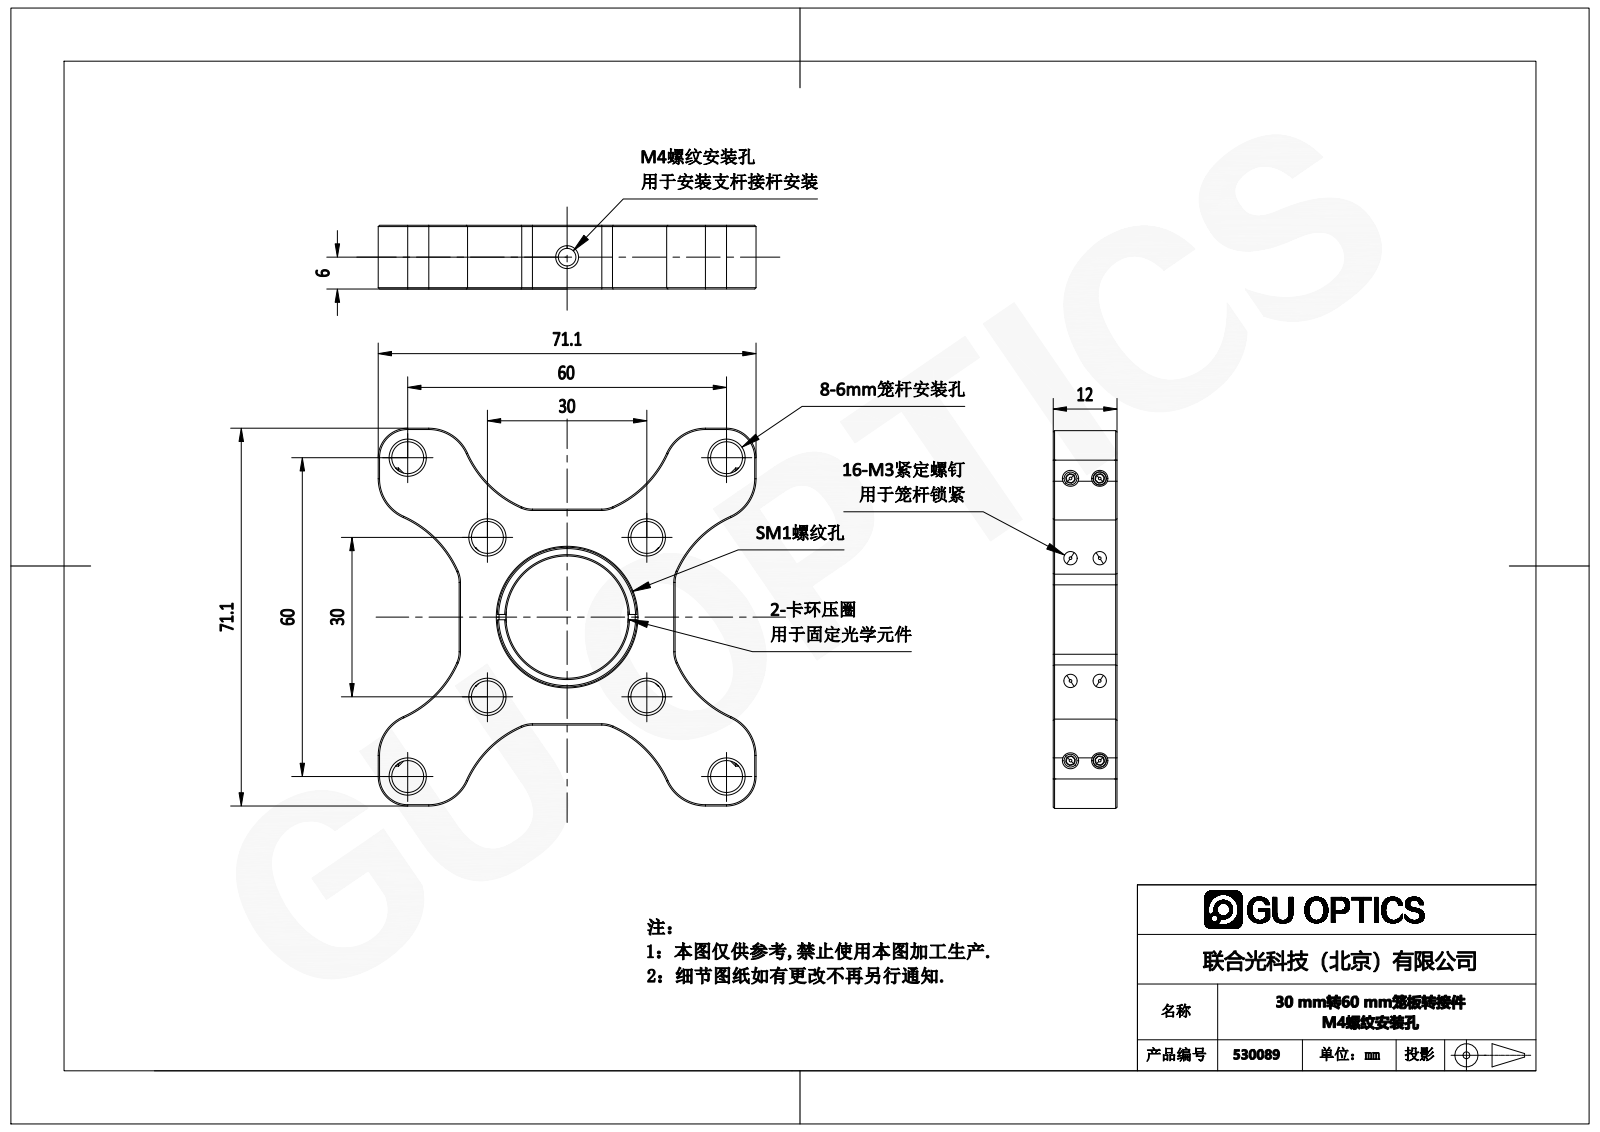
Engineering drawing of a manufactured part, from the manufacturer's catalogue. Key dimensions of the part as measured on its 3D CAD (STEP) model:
Part name (STEP PRODUCT): 2.3.1.3_L60B-6030_60mm笼式转30mm笼式系统转接笼板，带M4螺纹安装孔
STEP written by: SolidWorks 2018 (AUTOMOTIVE_DESIGN)
Units: millimetres
Bodies: 0 solids, 490 faces (128 planar, 108 cylindrical, 254 other)
Overall size (bounding box): 71.1 × 71.1 × 12
Round holes (diameter × count): ⌀2.5 ×8, ⌀6 ×8, ⌀3.3 ×1, ⌀23.01 ×1, ⌀25.65 ×1
Round bosses / shafts (diameter × count): ⌀3 ×6
Partial cylindrical surfaces — rounded edges, fillets, slot ends (radius × count): R5 ×8, R8 ×8, R20 ×8, R5.55 ×4
Main face-to-face distances: 12, 15.23, 55.87, 40.64, 2, 10, 71.1, 8, 1.5, 10.77
Hole centre spacings: 21.21, 47.43, 42.43, 5.5, 15, 15.98, 30, 38.1
